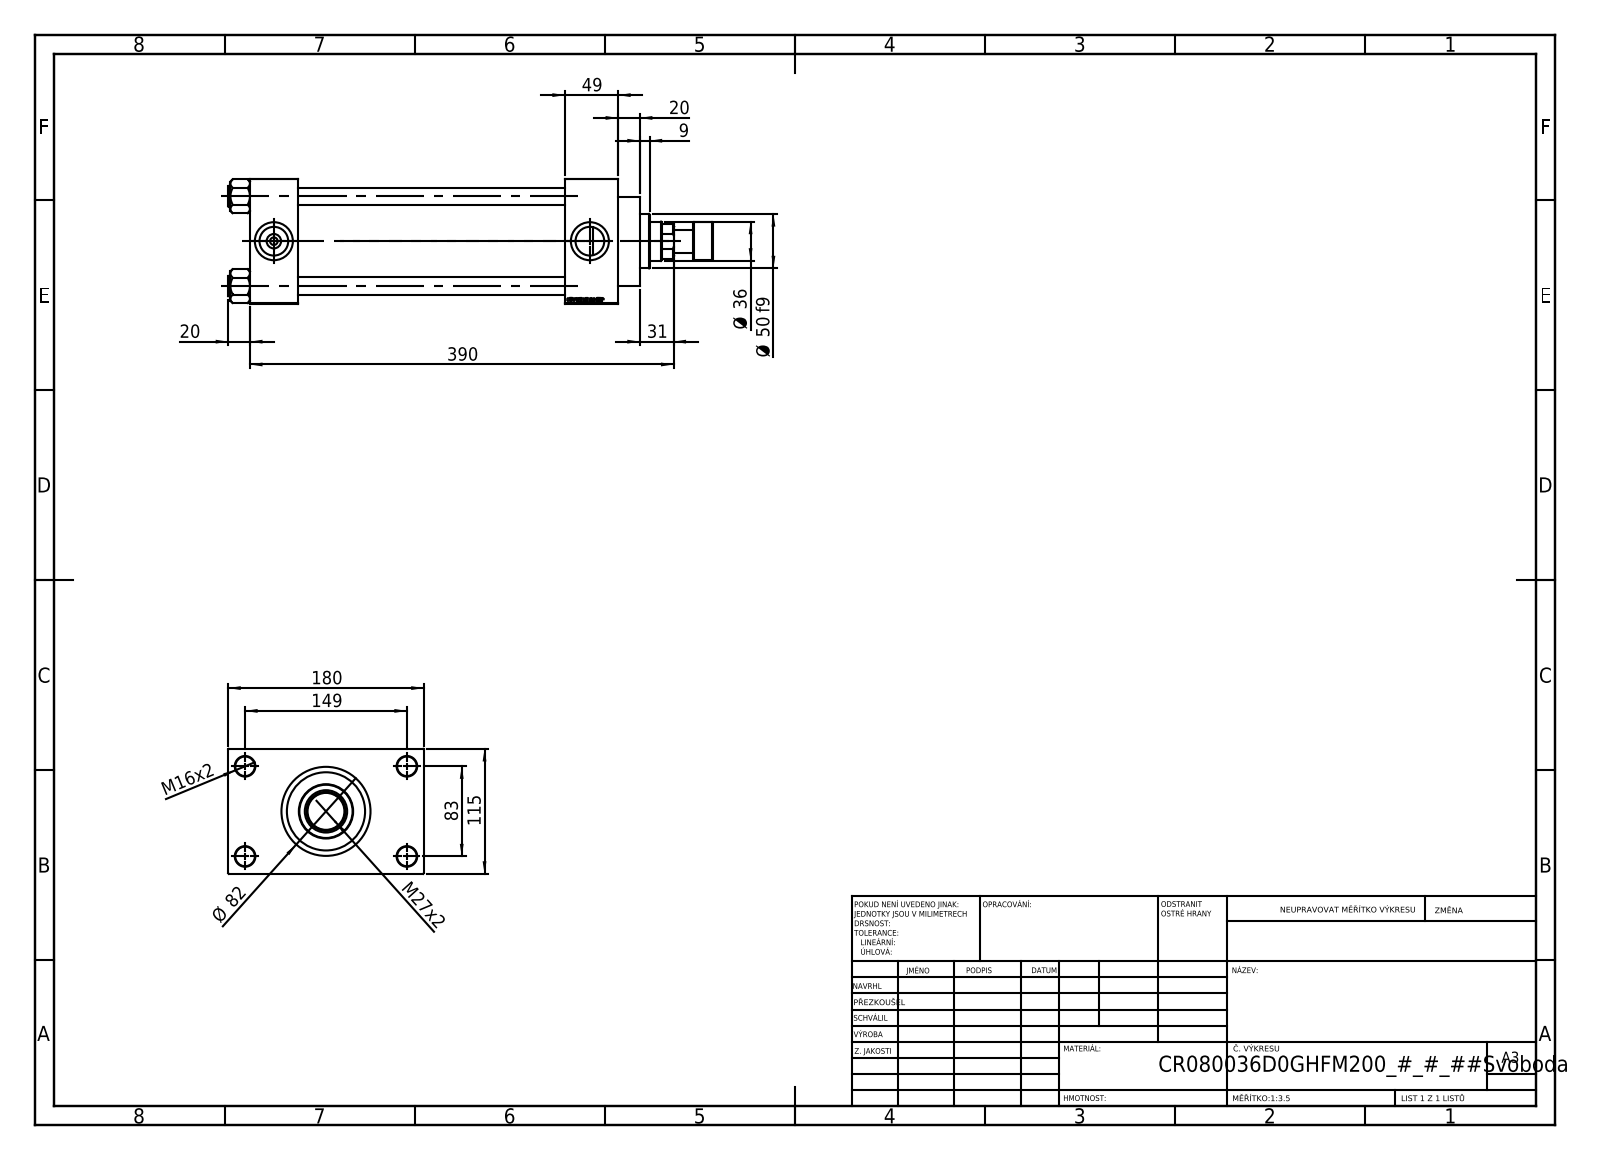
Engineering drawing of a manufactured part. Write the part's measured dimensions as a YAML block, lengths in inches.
part_name: "V215CR_D_Body; V215CR_VCP_D; NUT_M5_D; V215CR_D_TYCINKA (+2 more)"
step_written_by: "SolidWorks 2019 (CONFIG_CONTROL_DESIGN)"
units: inches
bodies: {solids: 12, faces: 1165, planar: 549, cylindrical: 92, other: 524}
overall_size: [17.559, 7.087, 4.528]
volume: 150.9
surface_area: 701.5
round_holes:
  - {diameter: 0.63, count: 4}
  - {diameter: 0.709, count: 4}
  - {diameter: 0.276, count: 2}
  - {diameter: 1.041, count: 2}
  - {diameter: 1.378, count: 2}
  - {diameter: 1.004, count: 1}
  - {diameter: 1.417, count: 1}
  - {diameter: 1.535, count: 1}
  - {diameter: 2.402, count: 1}
  - {diameter: 2.835, count: 1}
  - {diameter: 3.15, count: 1}
round_bosses_or_shafts:
  - {diameter: 0.748, count: 4}
  - {diameter: 3.386, count: 1}
  - {diameter: 3.228, count: 1}
  - {diameter: 1.969, count: 1}
  - {diameter: 1.378, count: 1}
  - {diameter: 0.827, count: 1}
face_to_face_distances: [4.528, 9.685, 1.929, 11.614, 1.732, 11.417, 13.346, 1.28, 5.807, 7.087]
hole_center_spacings: [1.305, 2.302, 3.256, 3.357, 3.513, 4.561, 5.607, 3.268]
